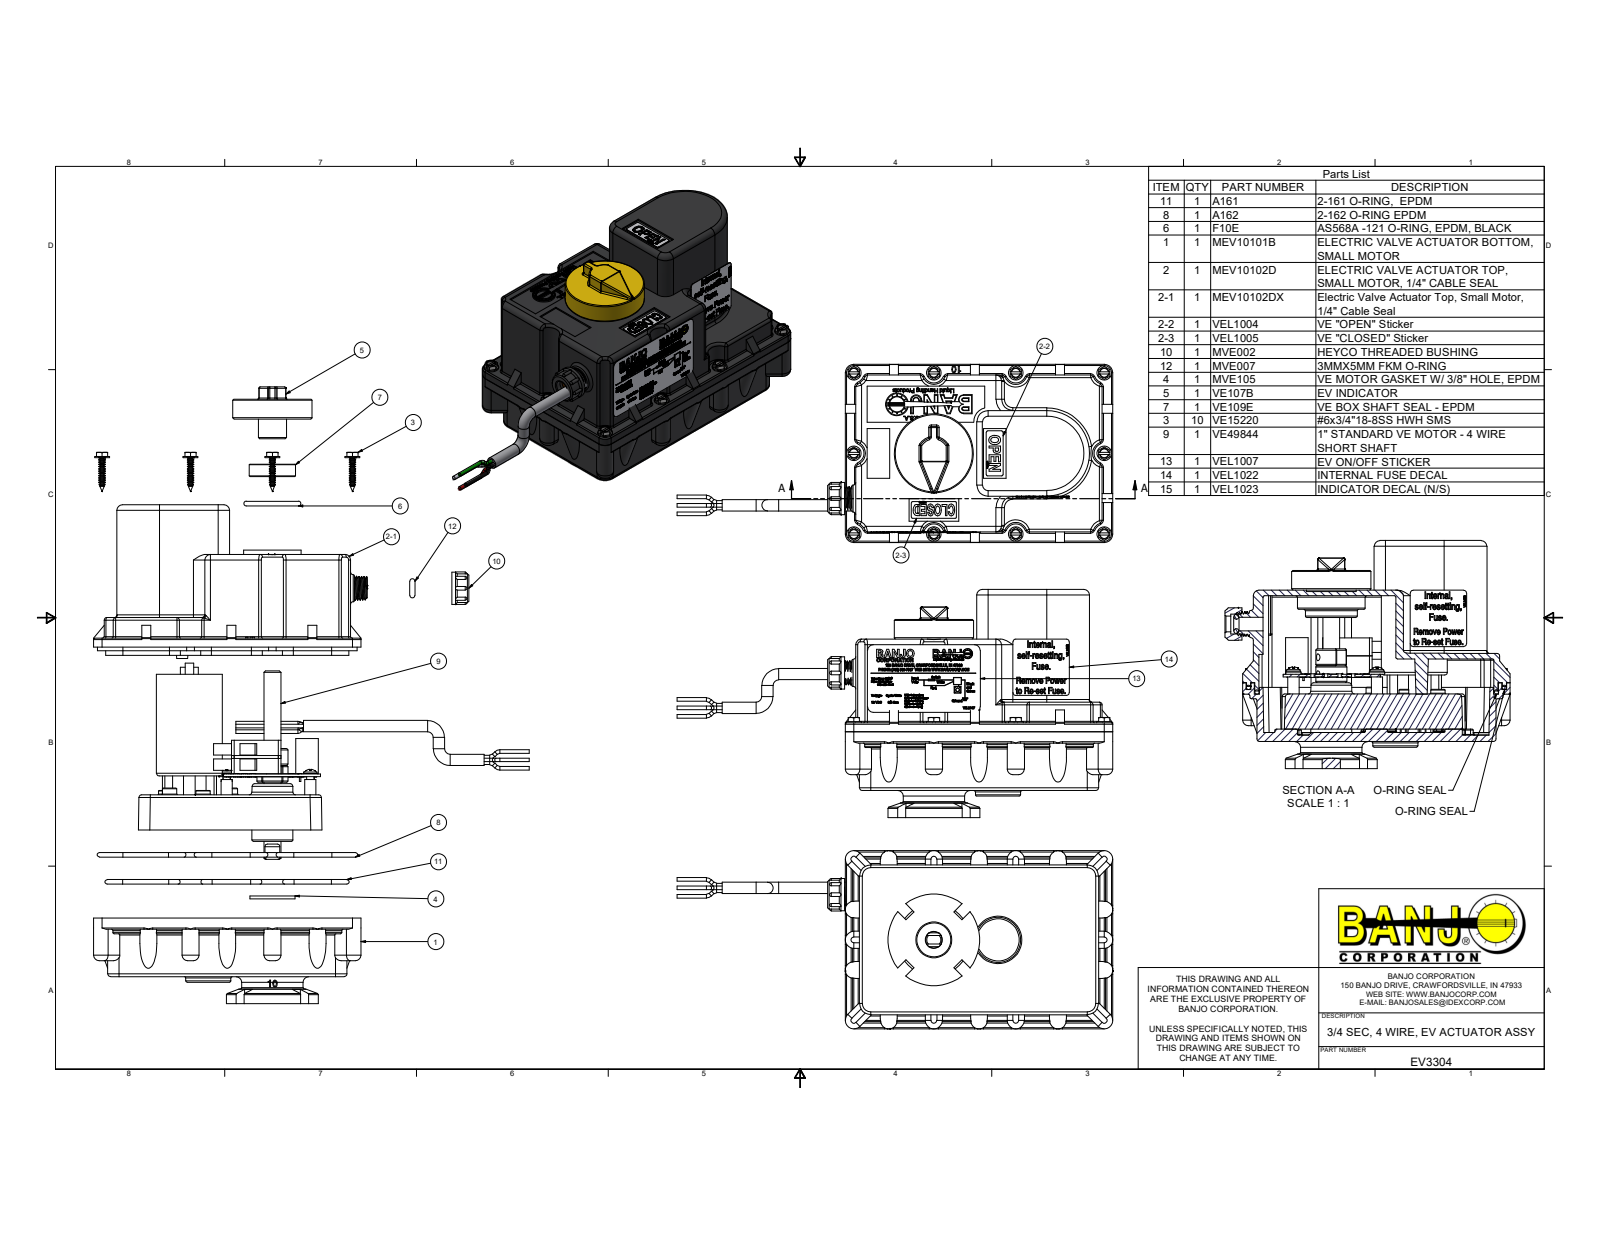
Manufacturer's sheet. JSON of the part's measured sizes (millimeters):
{"part_name": "EV3304; MEV10101B; MEV10102D; MEV10102DX (+8 more)", "step_written_by": "Autodesk Inventor 2022 (AUTOMOTIVE_DESIGN)", "units": "millimeters", "bodies": {"solids": 42, "faces": 10344, "planar": 5374, "cylindrical": 1183, "other": 3787}, "overall_size": [245.3, 128.4, 100.3], "volume_mm3": 567000, "surface_area_mm2": 255900, "round_holes": [[2.8, 10], [4.1, 10], [5.1, 10], [1.3, 8], [2, 8], [1.2, 6], [3, 6], [3.8, 6], [4.5, 6], [0.4, 4], [1, 3], [4.3, 3]], "round_bosses_or_shafts": [[2, 19], [8.3, 10], [3.5, 10], [2.6, 8], [6.4, 7], [8, 4], [0.6, 4], [8.7, 3]], "partial_cylinders_radius": [[0.8, 121], [0.5, 62], [1.5, 47], [0.9, 43], [3.2, 28], [8, 24], [12.7, 24], [9.9, 16]], "face_to_face_distances": [3.2, 85.2, 27.9, 5.1, 20.1, 26, 82, 33, 65.2, 1.1], "hole_center_spacings": [42.7, 52.3, 42.8, 45.3, 60.4, 2.8, 12.5, 30.2]}
